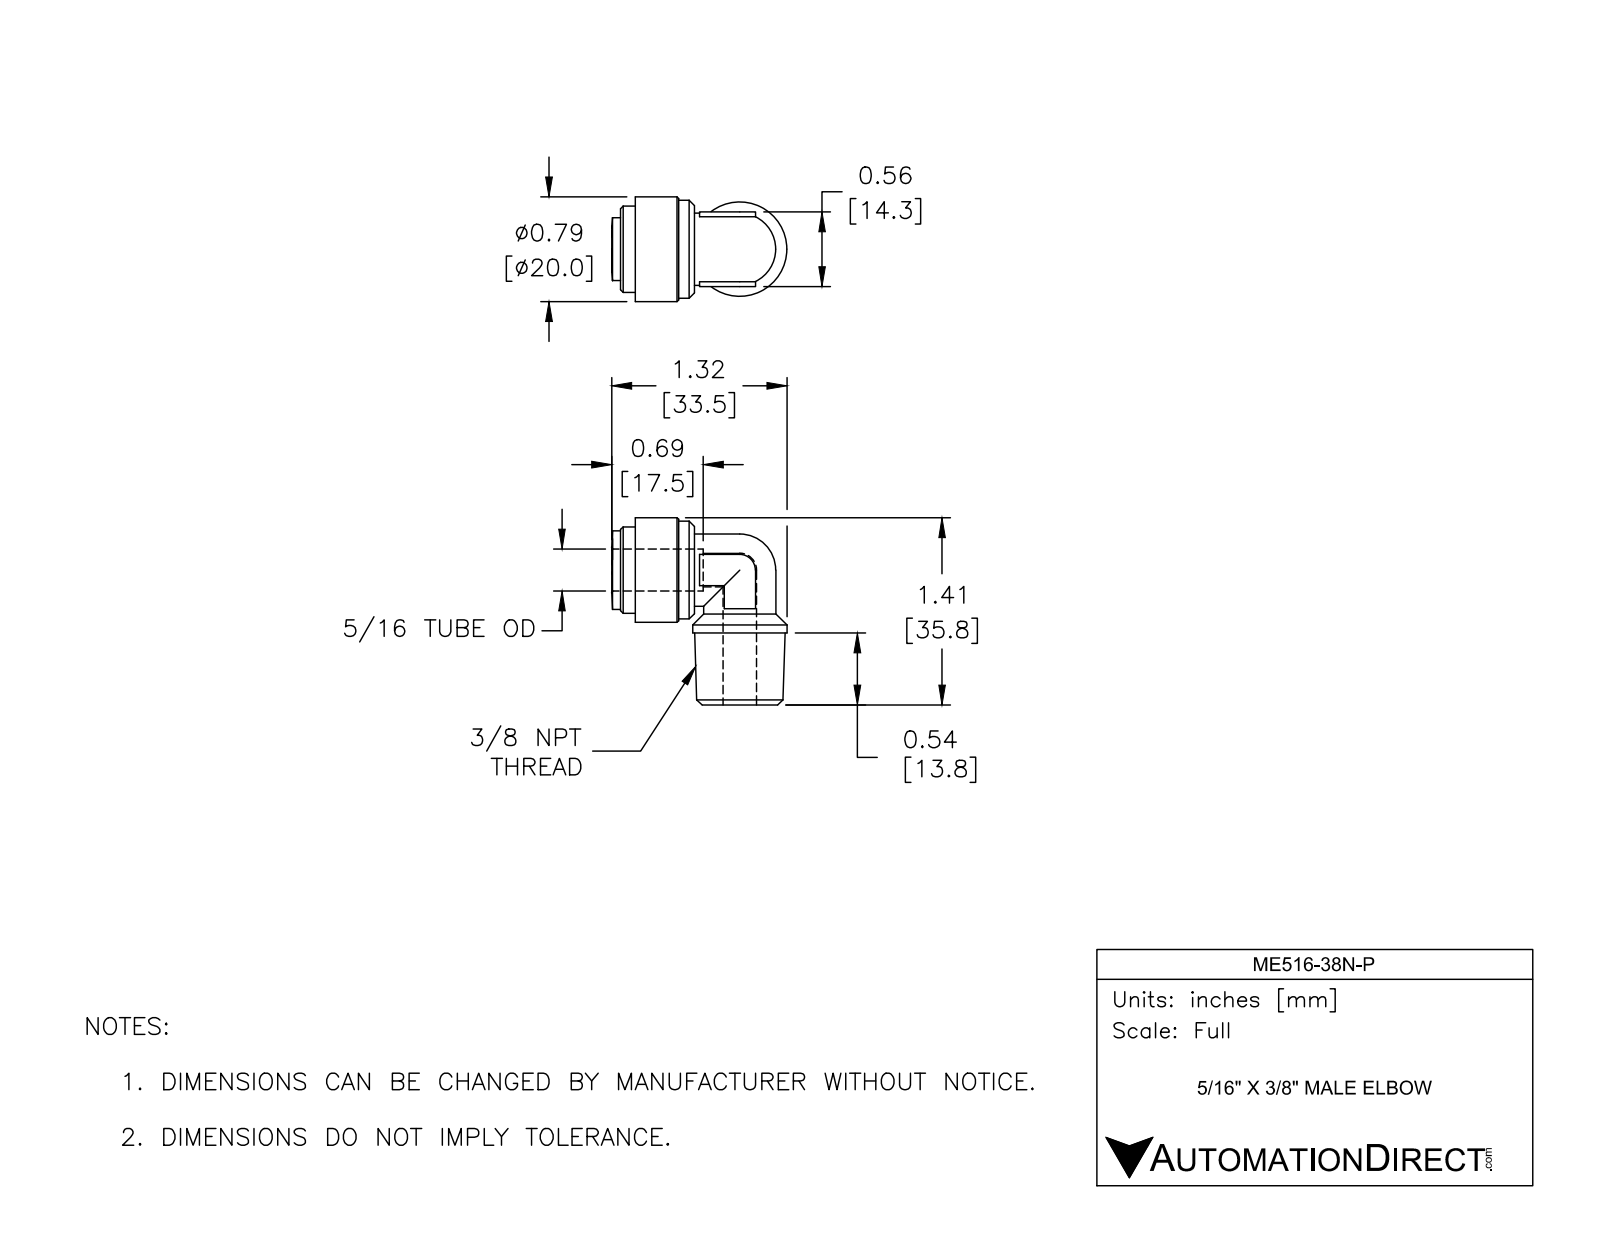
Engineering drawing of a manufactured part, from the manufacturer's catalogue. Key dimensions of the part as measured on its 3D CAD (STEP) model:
Part name (STEP PRODUCT): ME516-38N-P
STEP written by: SolidWorks 2017 (AUTOMOTIVE_DESIGN)
Units: inches
Bodies: 1 solid, 63 faces (21 planar, 20 cylindrical, 22 other)
Overall size (bounding box): 1.409 × 1.319 × 0.787
Volume: 0.531 in³ · Surface area: 6.622 in²
Round holes (diameter × count): ⌀0.252 ×2, ⌀0.315 ×1
Round bosses / shafts (diameter × count): ⌀0.543 ×2, ⌀0.787 ×1, ⌀0.736 ×1, ⌀0.709 ×1, ⌀0.65 ×1
Partial cylindrical surfaces — rounded edges, fillets, slot ends (radius × count): R0.118 ×1
Main face-to-face distances: 0.563, 0.445, 0.11, 0.555, 0.185, 0.437, 0.327, 0.118, 0.543, 0.622
